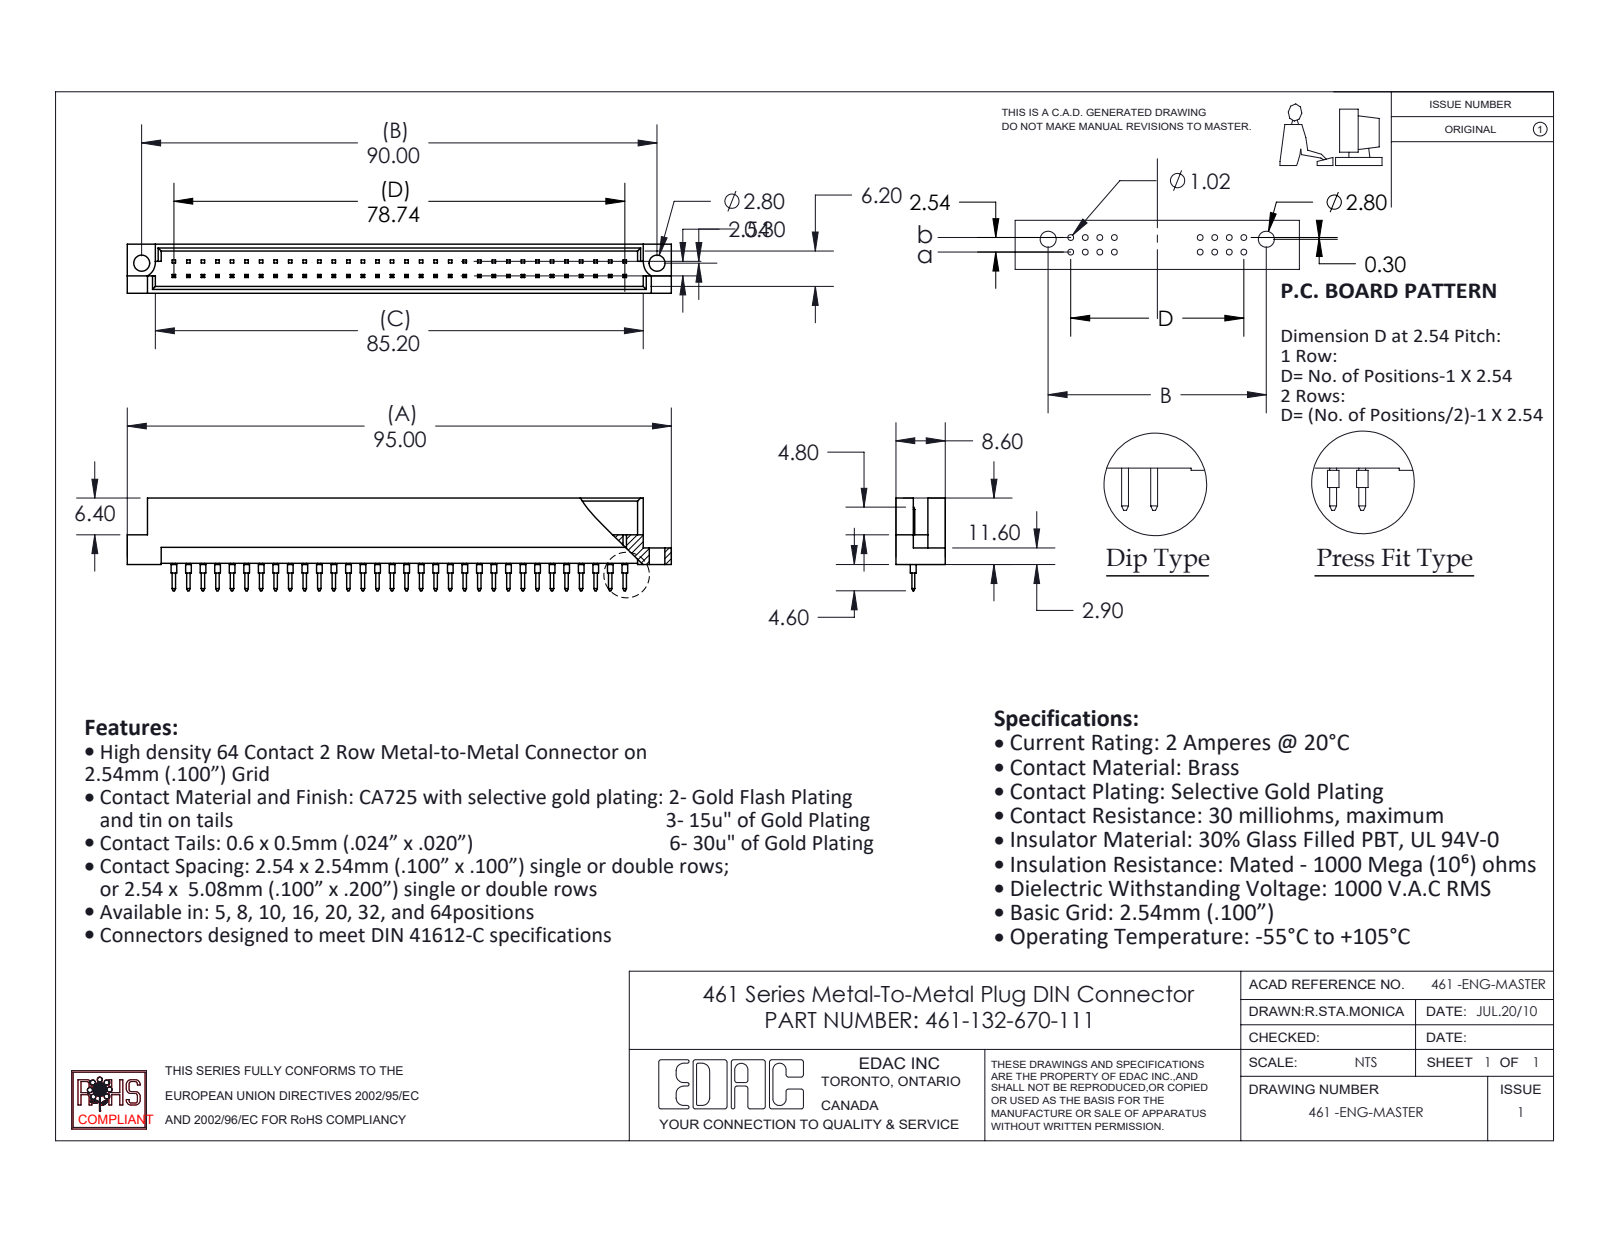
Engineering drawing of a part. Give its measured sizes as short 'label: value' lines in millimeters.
name: 461 Part_64; 461-290_70; 461-132-670-111
written by: SolidWorks 2020 (CONFIG_CONTROL_DESIGN)
unit: mm
bodies: 33 solids, 1009 faces (938 planar, 71 cylindrical, 0 other)
size: 95 × 16.2 × 8.6
volume: 4 816 mm³; area: 6 763 mm²
holes: 2× ⌀2.8
bosses: 32× ⌀1
rounds: 2× R2.8
face distances: 1.2, 7.4, 8.6, 6.2, 5, 3.28, 5.32, 2.08, 4.12, 2.78
hole spacings: 90
